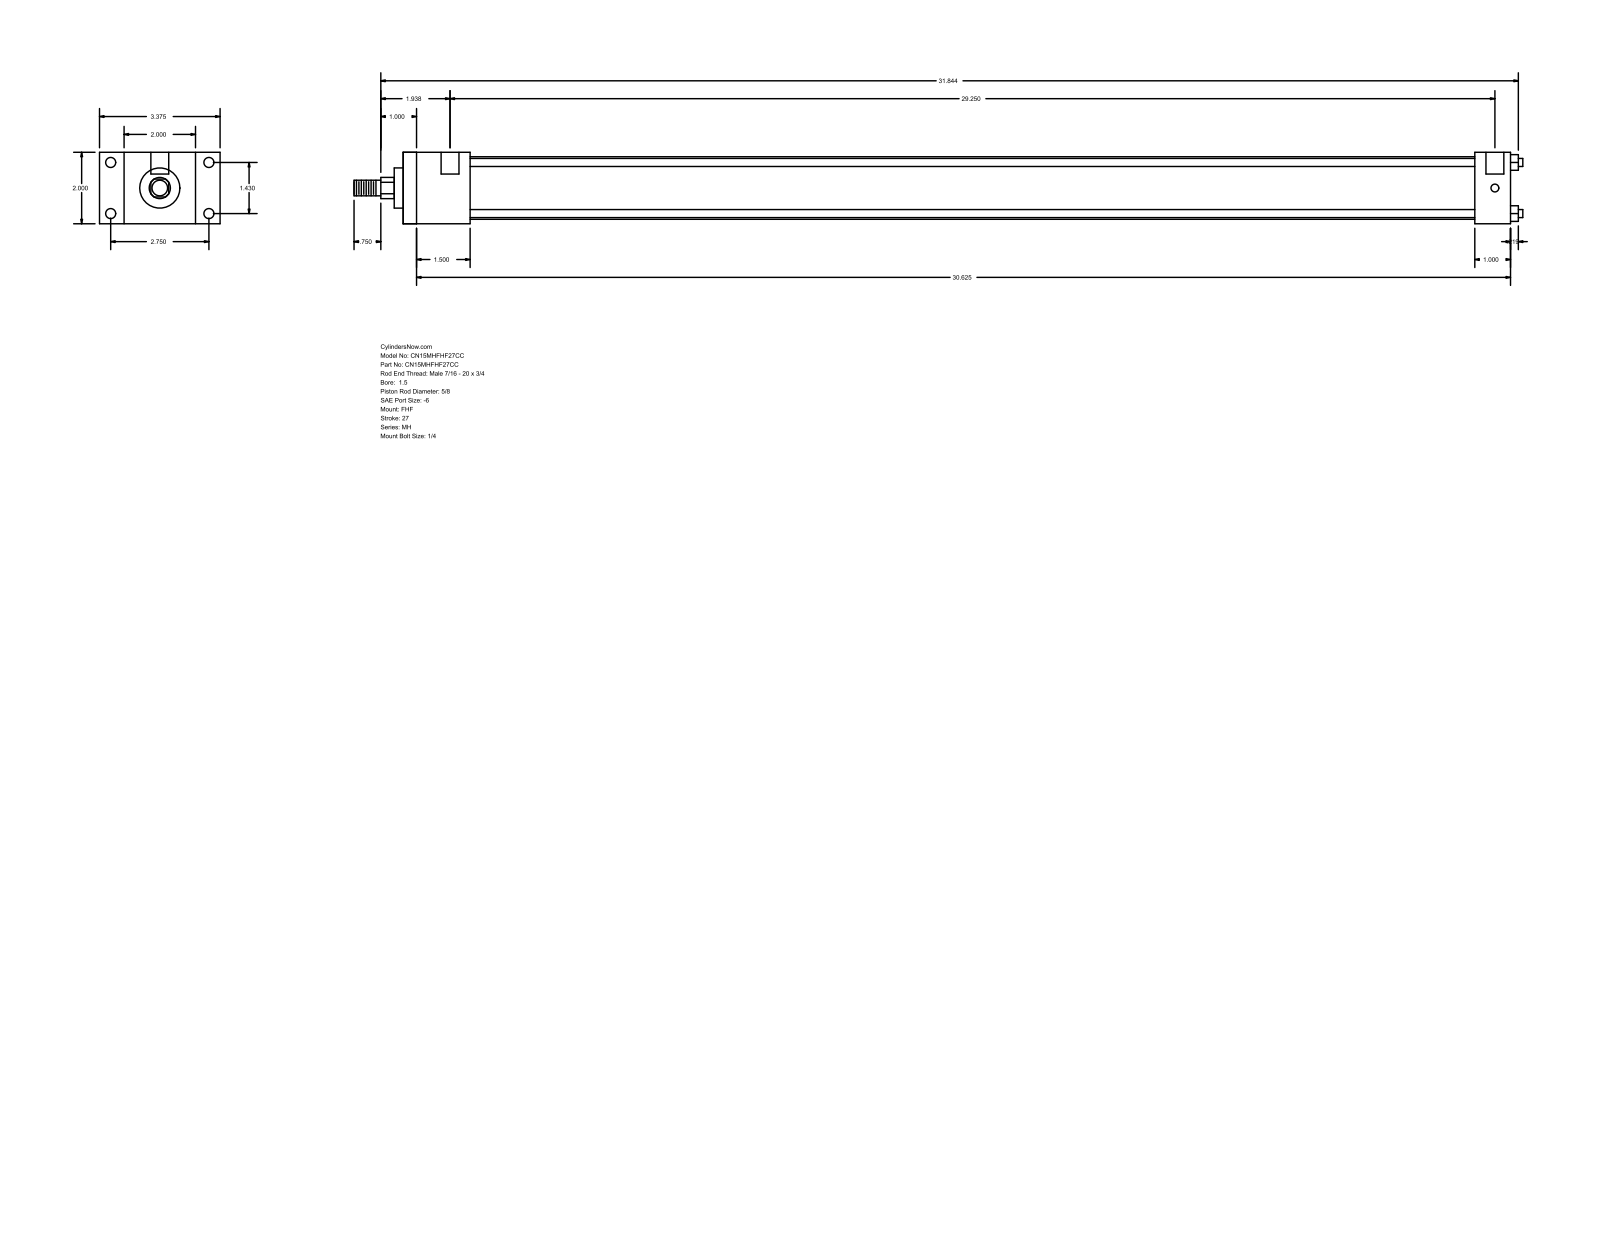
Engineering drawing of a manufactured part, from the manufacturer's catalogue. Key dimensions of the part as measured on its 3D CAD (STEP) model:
Part name (STEP PRODUCT): MH_FHF__0150_0.625
STEP written by: GSSL Pune (CONFIG_CONTROL_DESIGN)
Units: millimetres
Bodies: 0 solids, 88 faces (60 planar, 28 cylindrical, 0 other)
Overall size (bounding box): 831.06 × 85.72 × 50.8
Round holes (diameter × count): ⌀5.56 ×4, ⌀7.14 ×4, ⌀12.7 ×2
Round bosses / shafts (diameter × count): ⌀5.71 ×4, ⌀44.45 ×1, ⌀28.57 ×1, ⌀15.88 ×1, ⌀11.11 ×1
Partial cylindrical surfaces — rounded edges, fillets, slot ends (radius × count): R7.54 ×1
Main face-to-face distances: 50.8, 17.46, 68.26, 47.62, 85.72, 787.39, 739.77, 762, 714.38, 25.39
Hole centre spacings: 36.32, 69.84, 78.72, 746.12, 3.17, 742.95
